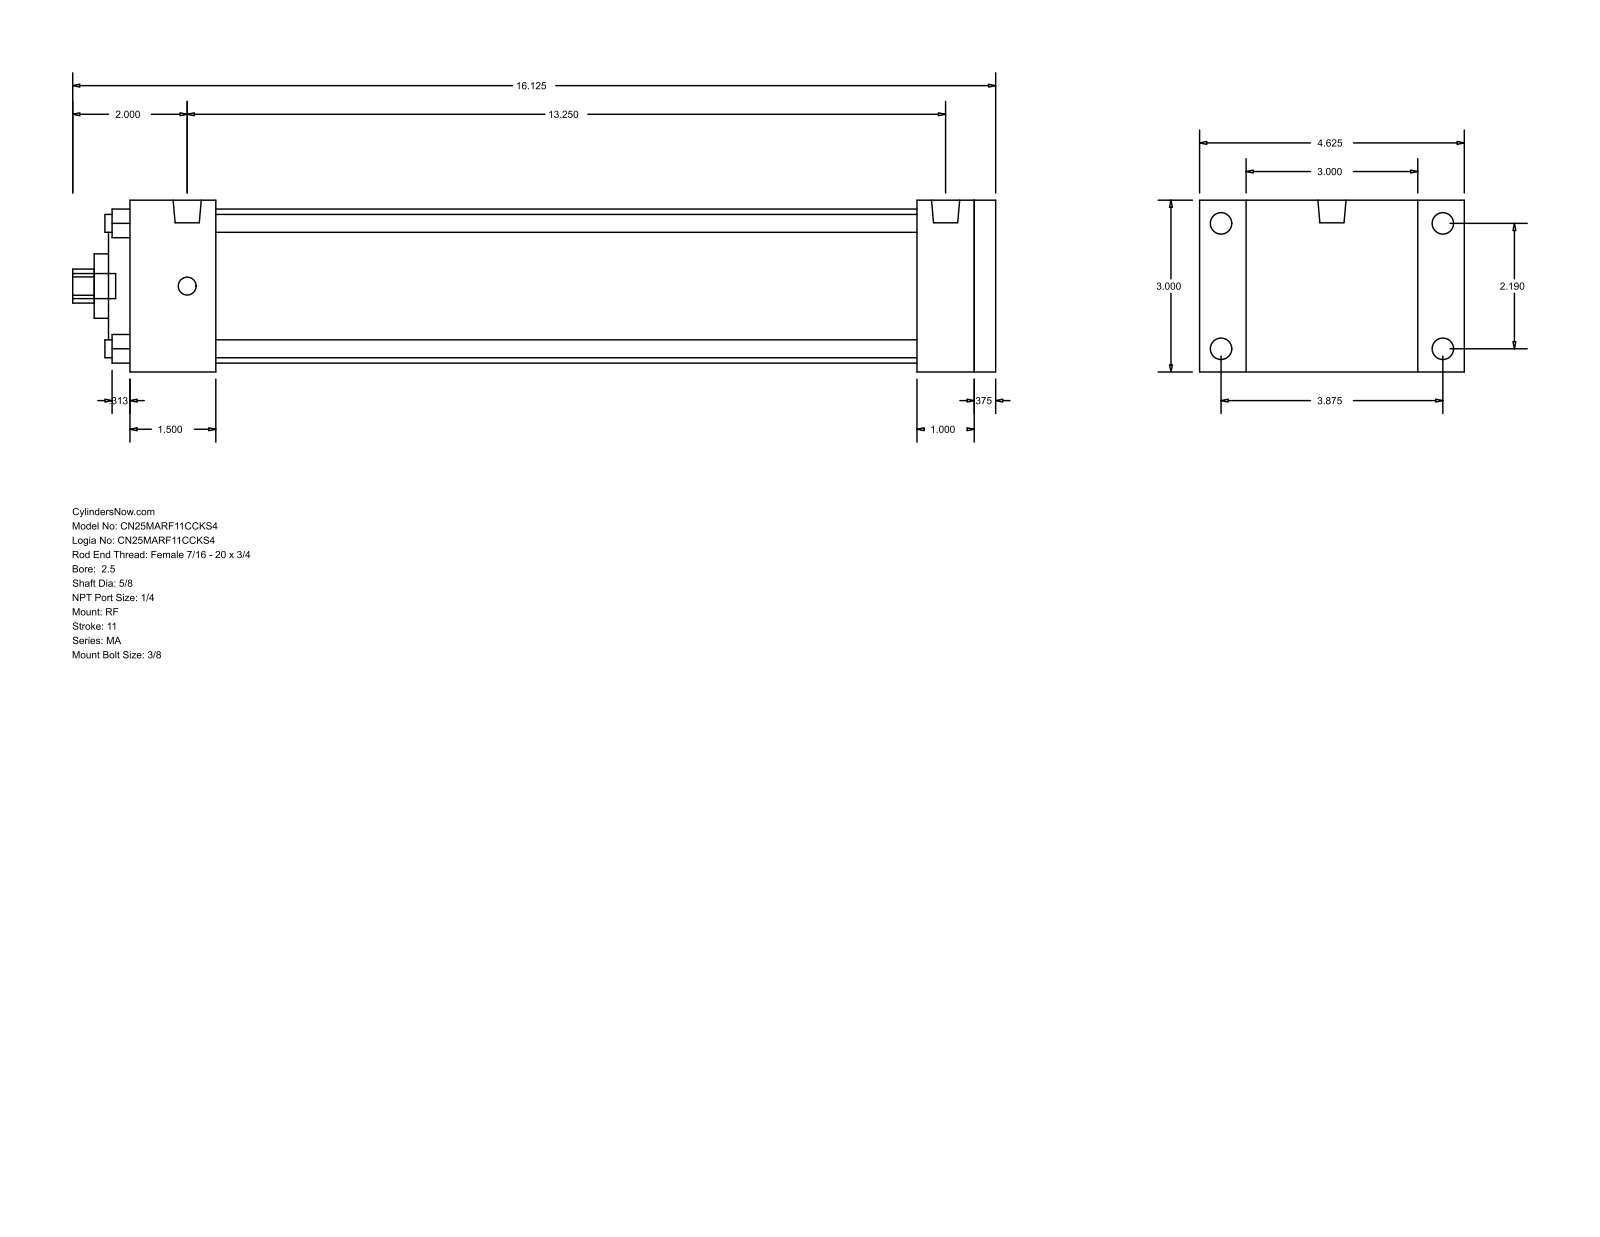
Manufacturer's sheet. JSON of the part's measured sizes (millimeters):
{"part_name": "MA_RF__0250_0.625", "step_written_by": "GSSL Pune (CONFIG_CONTROL_DESIGN)", "units": "millimeters", "bodies": {"solids": 0, "faces": 94, "planar": 65, "cylindrical": 29, "other": 0}, "overall_size": [409.57, 117.47, 76.2], "round_holes": [[7.94, 4], [15.88, 1], [28.57, 1], [50.8, 1], [68.33, 1]], "round_bosses_or_shafts": [[9.53, 4], [7.94, 4], [12.49, 2], [11.11, 1]], "partial_cylinders_radius": [[7.54, 1]], "face_to_face_distances": [76.2, 384.17, 9.52, 374.65, 25.4, 38.1, 349.25, 311.15, 336.55, 346.07], "hole_center_spacings": [39.33, 55.62, 78.66]}
